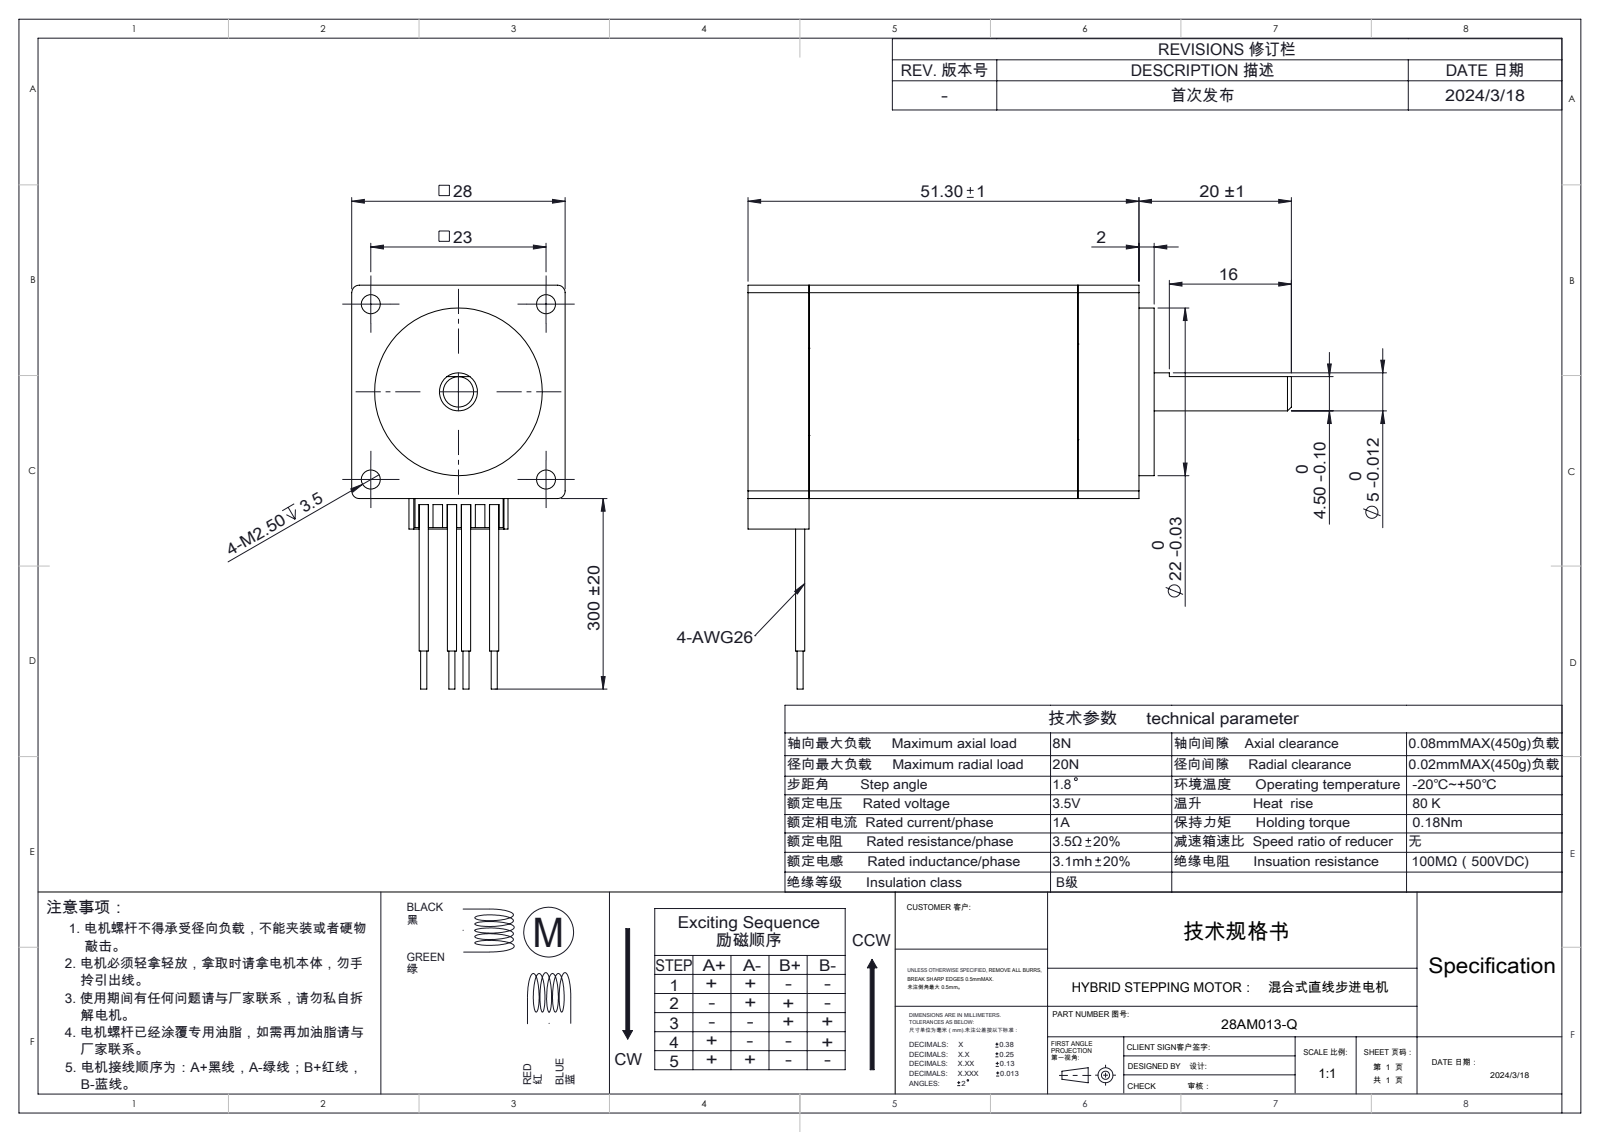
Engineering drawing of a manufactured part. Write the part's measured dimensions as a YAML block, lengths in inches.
part_name: "28AM018"
step_written_by: "SolidWorks 2024 (AUTOMOTIVE_DESIGN)"
units: inches
bodies: {solids: 2, faces: 137, planar: 72, cylindrical: 62, other: 3}
overall_size: [2.807, 2.087, 1.102]
volume: 2.422
surface_area: 20.8
round_holes:
  - {diameter: 0.098, count: 4}
  - {diameter: 0.197, count: 1}
round_bosses_or_shafts:
  - {diameter: 0.047, count: 4}
  - {diameter: 0.031, count: 4}
  - {diameter: 0.866, count: 1}
  - {diameter: 0.494, count: 1}
  - {diameter: 0.451, count: 1}
partial_cylinders:
  - {radius: 0.039, count: 4}
face_to_face_distances: [1.102, 1.39, 0.315, 1.705, 2.02, 0.079, 2.098, 1.783, 0.394, 0.073]
hole_center_spacings: [0.64, 0.906, 1.281]
